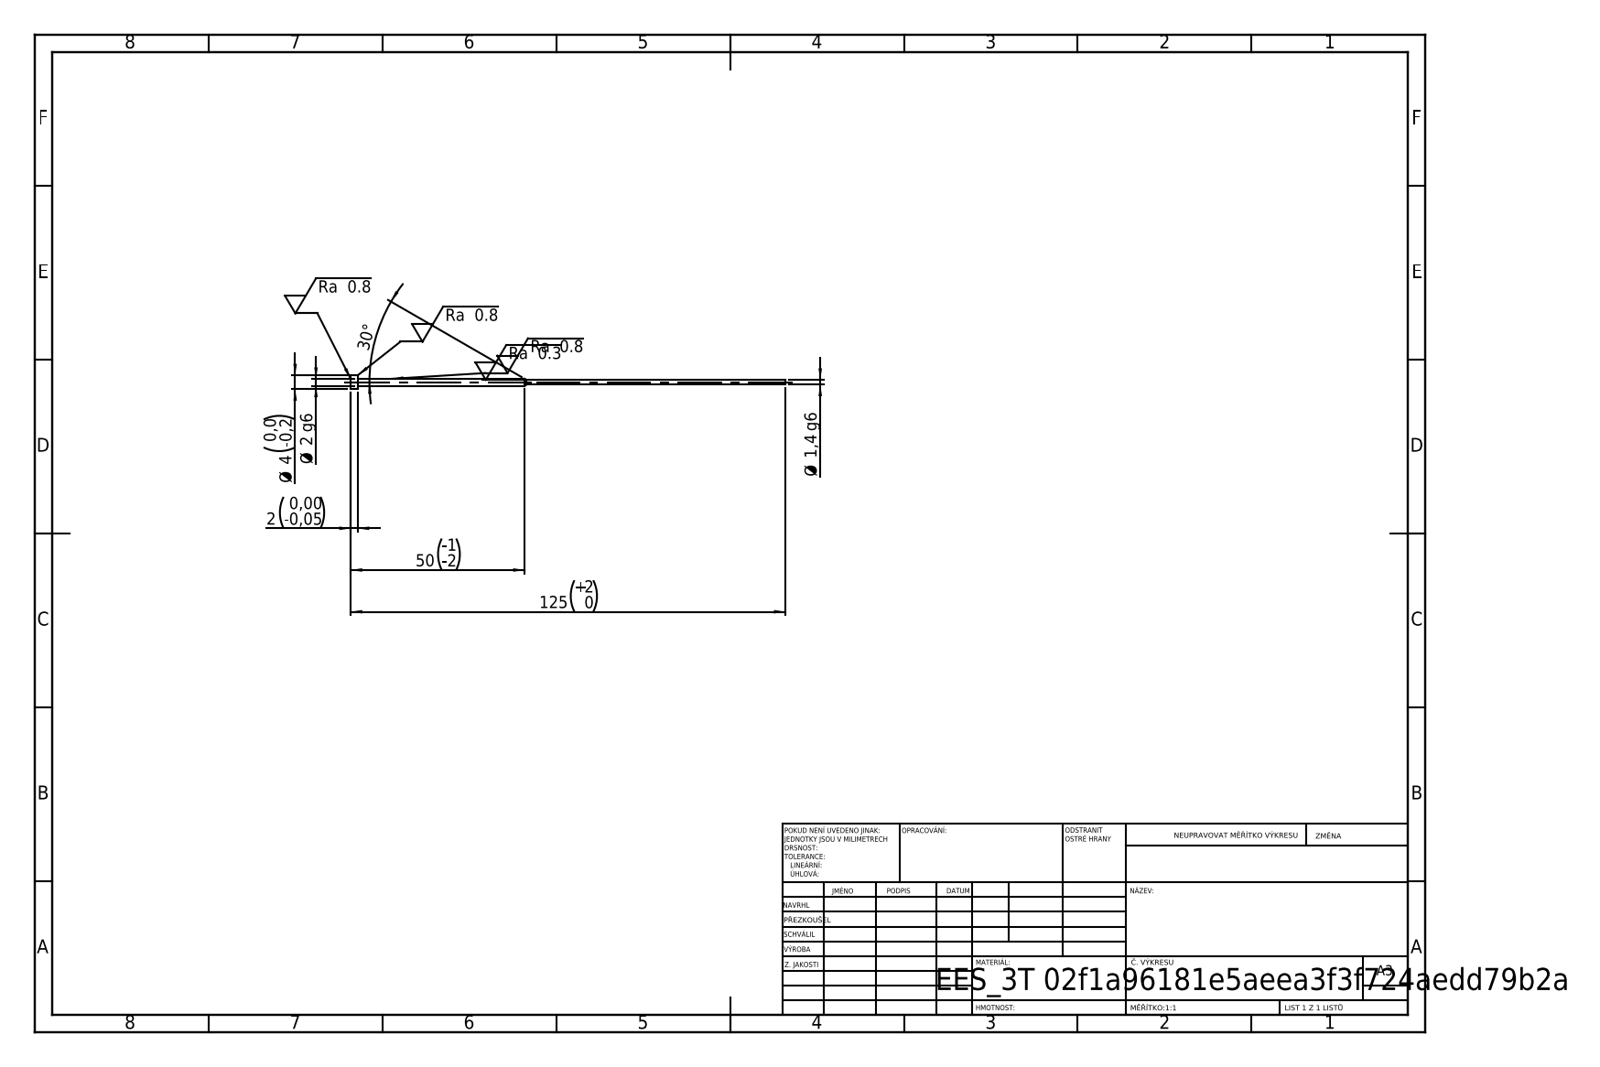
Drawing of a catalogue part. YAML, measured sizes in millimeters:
step_written_by: "SolidWorks 2019 (CONFIG_CONTROL_DESIGN)"
units: millimeters
bodies: {solids: 1, faces: 11, planar: 3, cylindrical: 6, other: 2}
overall_size: [125, 4, 4]
volume: 292
surface_area: 681
round_bosses_or_shafts:
  - {diameter: 4, count: 1}
  - {diameter: 2, count: 1}
  - {diameter: 1.4, count: 1}
face_to_face_distances: [2, 123, 125]
